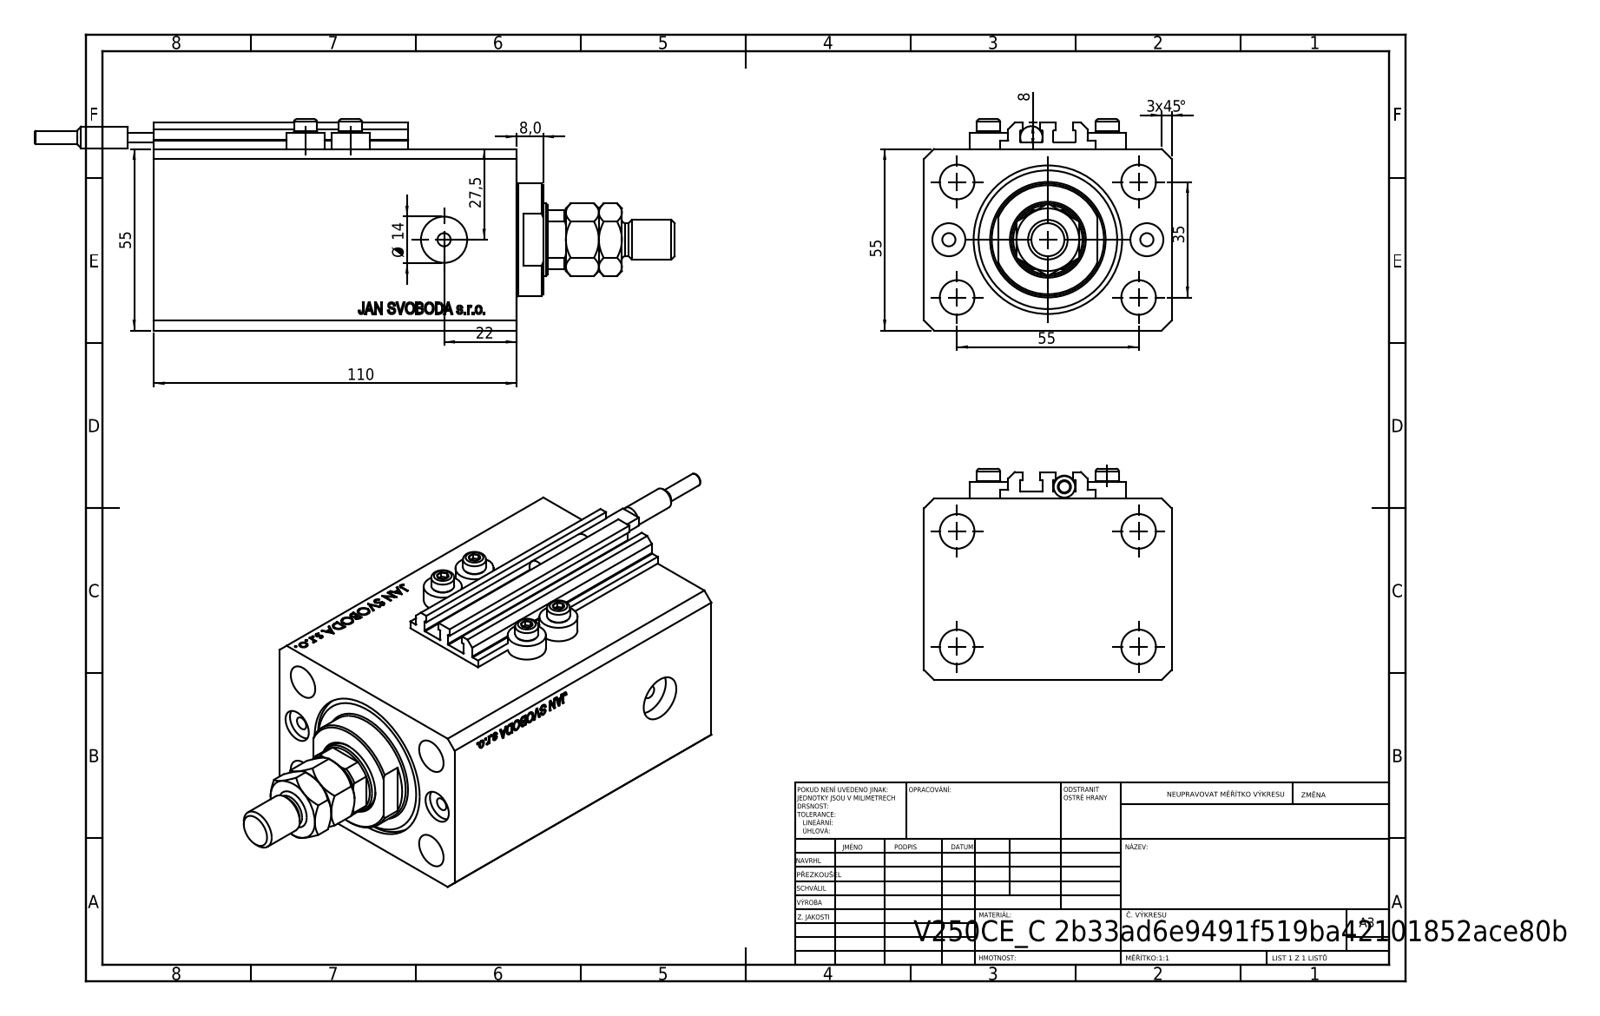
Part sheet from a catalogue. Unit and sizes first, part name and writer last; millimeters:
Units: millimetres
Overall size (bounding box): 193.9 × 75 × 64
Round holes (diameter × count): ⌀4 ×8, ⌀10.5 ×5, ⌀10 ×2, ⌀14 ×2, ⌀22 ×1, ⌀32 ×1, ⌀45 ×1
Round bosses / shafts (diameter × count): ⌀11.6 ×4, ⌀7 ×4, ⌀34 ×1, ⌀12 ×1, ⌀10 ×1, ⌀6.8 ×1, ⌀6.5 ×1, ⌀4 ×1
Partial cylindrical surfaces — rounded edges, fillets, slot ends (radius × count): R0.2 ×10, R10.5 ×1
Main face-to-face distances: 55, 75, 110, 82.9, 27.1, 9.9, 73, 100.1, 2.5, 3
Hole centre spacings: 17.68, 32.6, 60.1, 13.6, 30, 35, 36, 38.48
Volume: 417 630 mm³ · Surface area: 97 466 mm²
Bodies: 10 solids, 1108 faces (534 planar, 96 cylindrical, 478 other)
Part name (STEP PRODUCT): V250CE_C_VCP; MTA; SWITCH_V250CE; V250CE_VC_C (+2 more)
STEP written by: SolidWorks 2019 (CONFIG_CONTROL_DESIGN)
